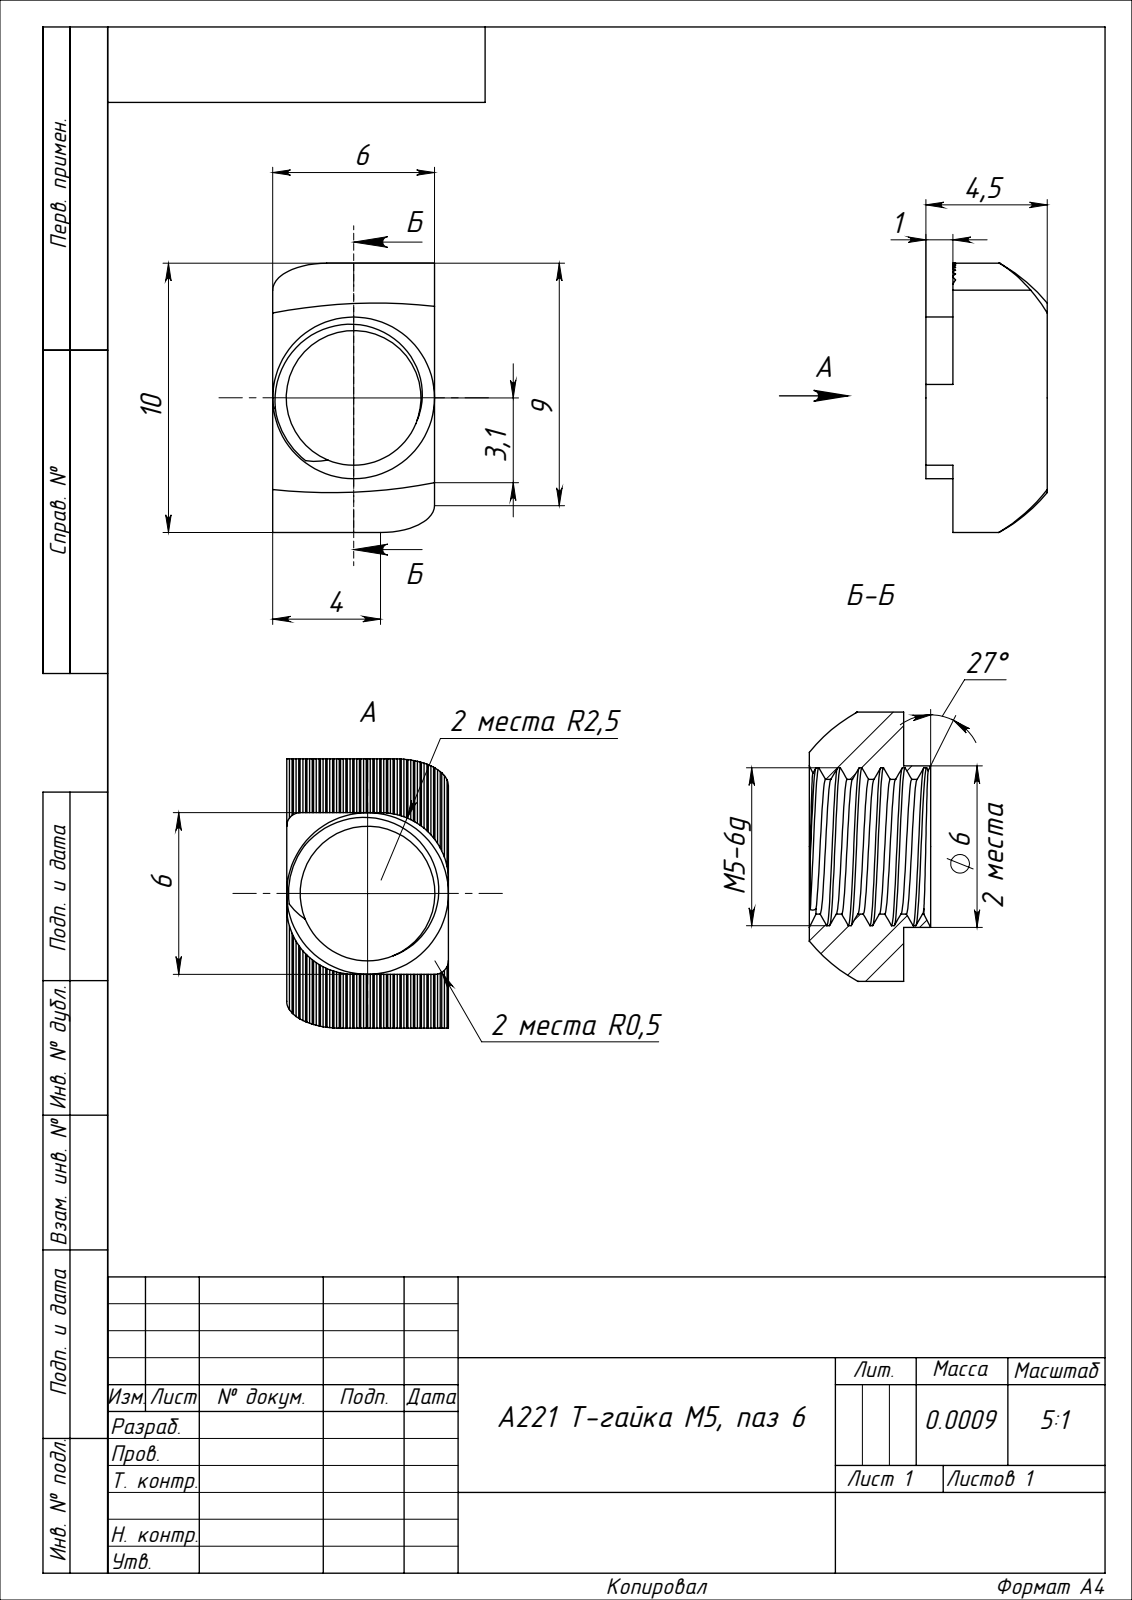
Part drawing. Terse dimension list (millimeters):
name: А221 Т-гайка М5, паз 6 (подробная модель)
written by: SolidWorks 2018 (AUTOMOTIVE_DESIGN)
unit: mm
bodies: 1 solid, 183 faces (156 planar, 16 cylindrical, 11 other)
size: 10.01 × 6 × 4.5
volume: 122 mm³; area: 313 mm²
holes: 1× ⌀5
rounds: 2× R0.5, 2× R2.5
face distances: 6, 0.53, 0.35, 1.06, 0.71, 2.65, 0.88, 2.3, 2.12, 2.83
